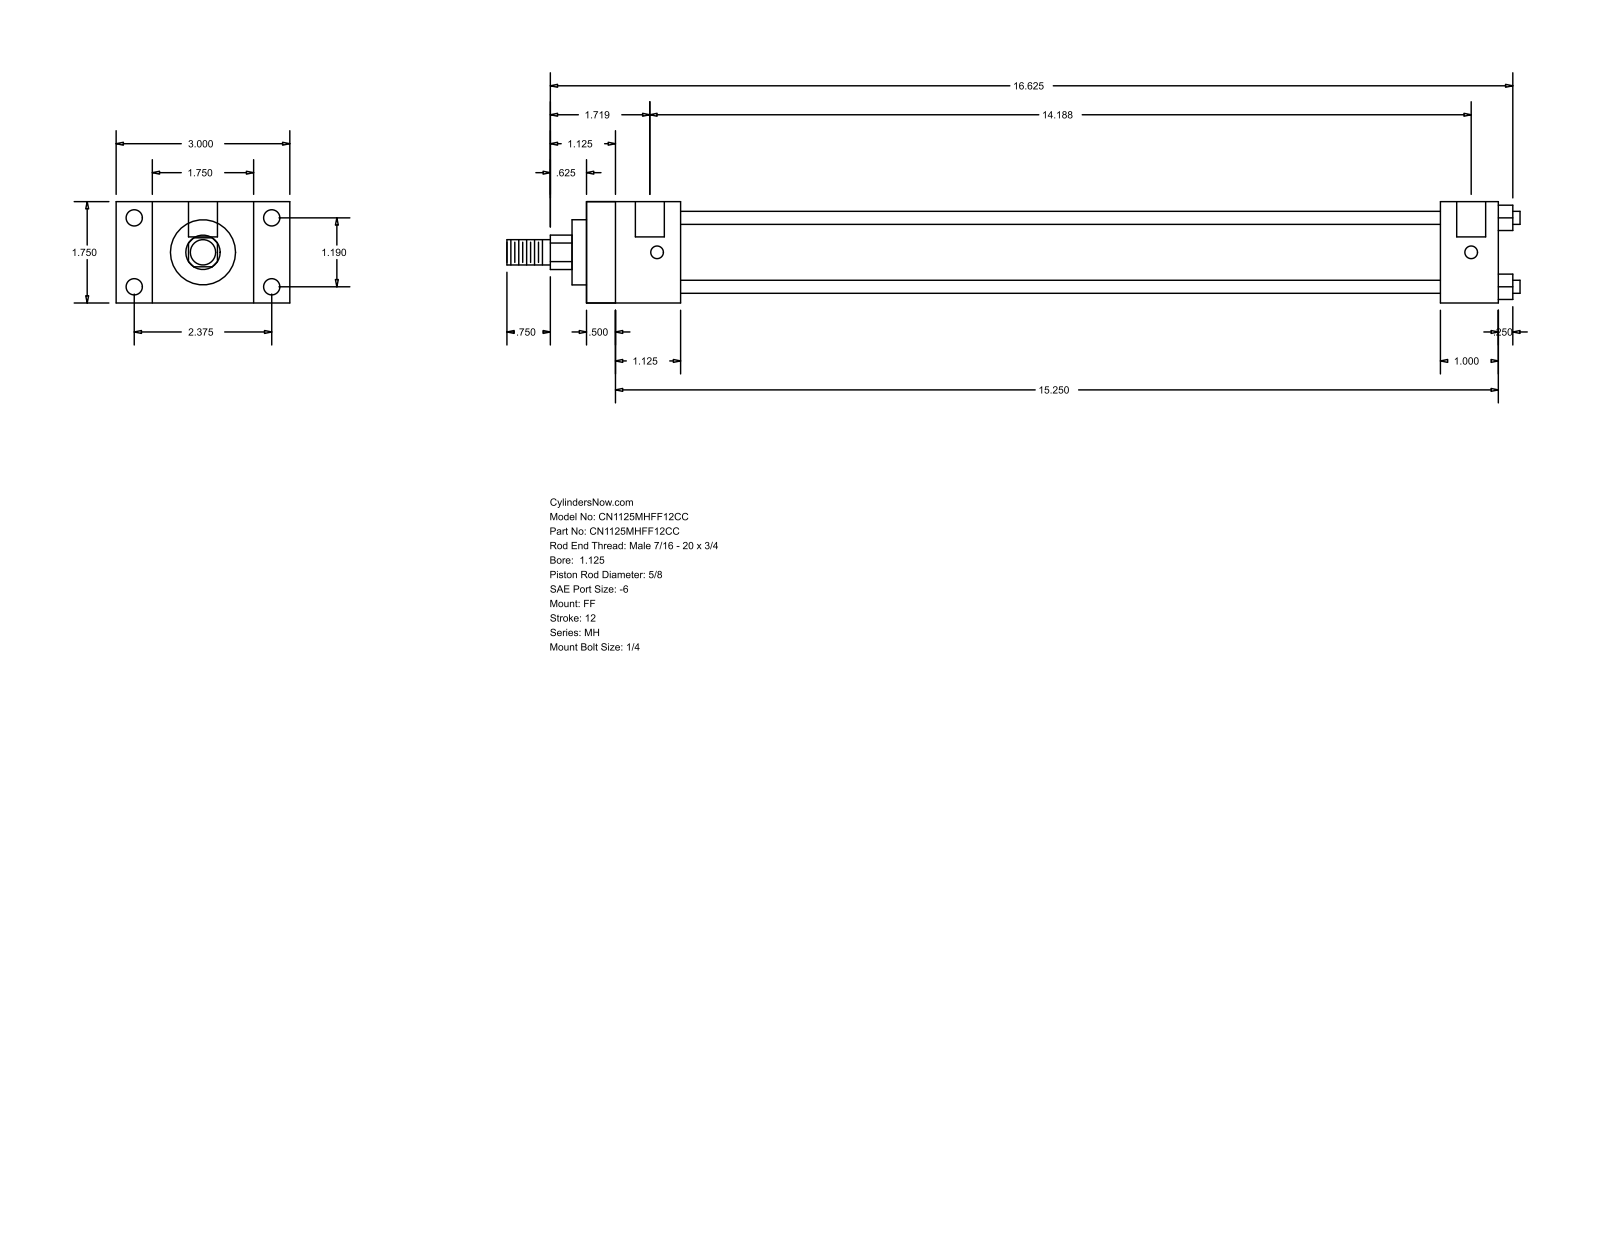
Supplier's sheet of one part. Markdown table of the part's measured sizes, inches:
| quantity | value |
| --- | --- |
| part name | MH_FF__0112_0.625 |
| STEP written by | GSSL Pune (CONFIG_CONTROL_DESIGN) |
| units | inches |
| bodies | 0 solids, 92 faces (64 planar, 28 cylindrical, 0 other) |
| overall size | 17.5 × 3 × 1.75 |
| round holes (diameter × count) | 0.219 × 4, 0.281 × 4, 0.5 × 2 |
| round bosses / shafts (diameter × count) | 0.225 × 4, 1.375 × 1, 1.125 × 1, 0.625 × 1, 0.437 × 1 |
| partial cylindrical surfaces (radius × count) | 0.297 × 1 |
| main face-to-face distances | 1.75, 15.75, 0.5, 15.25, 0.625, 1.125, 2.375, 1.625, 14.75, 14.25 |
| hole center spacings | 1.19, 2.375, 2.656, 14.063, 0.125, 14.187 |
